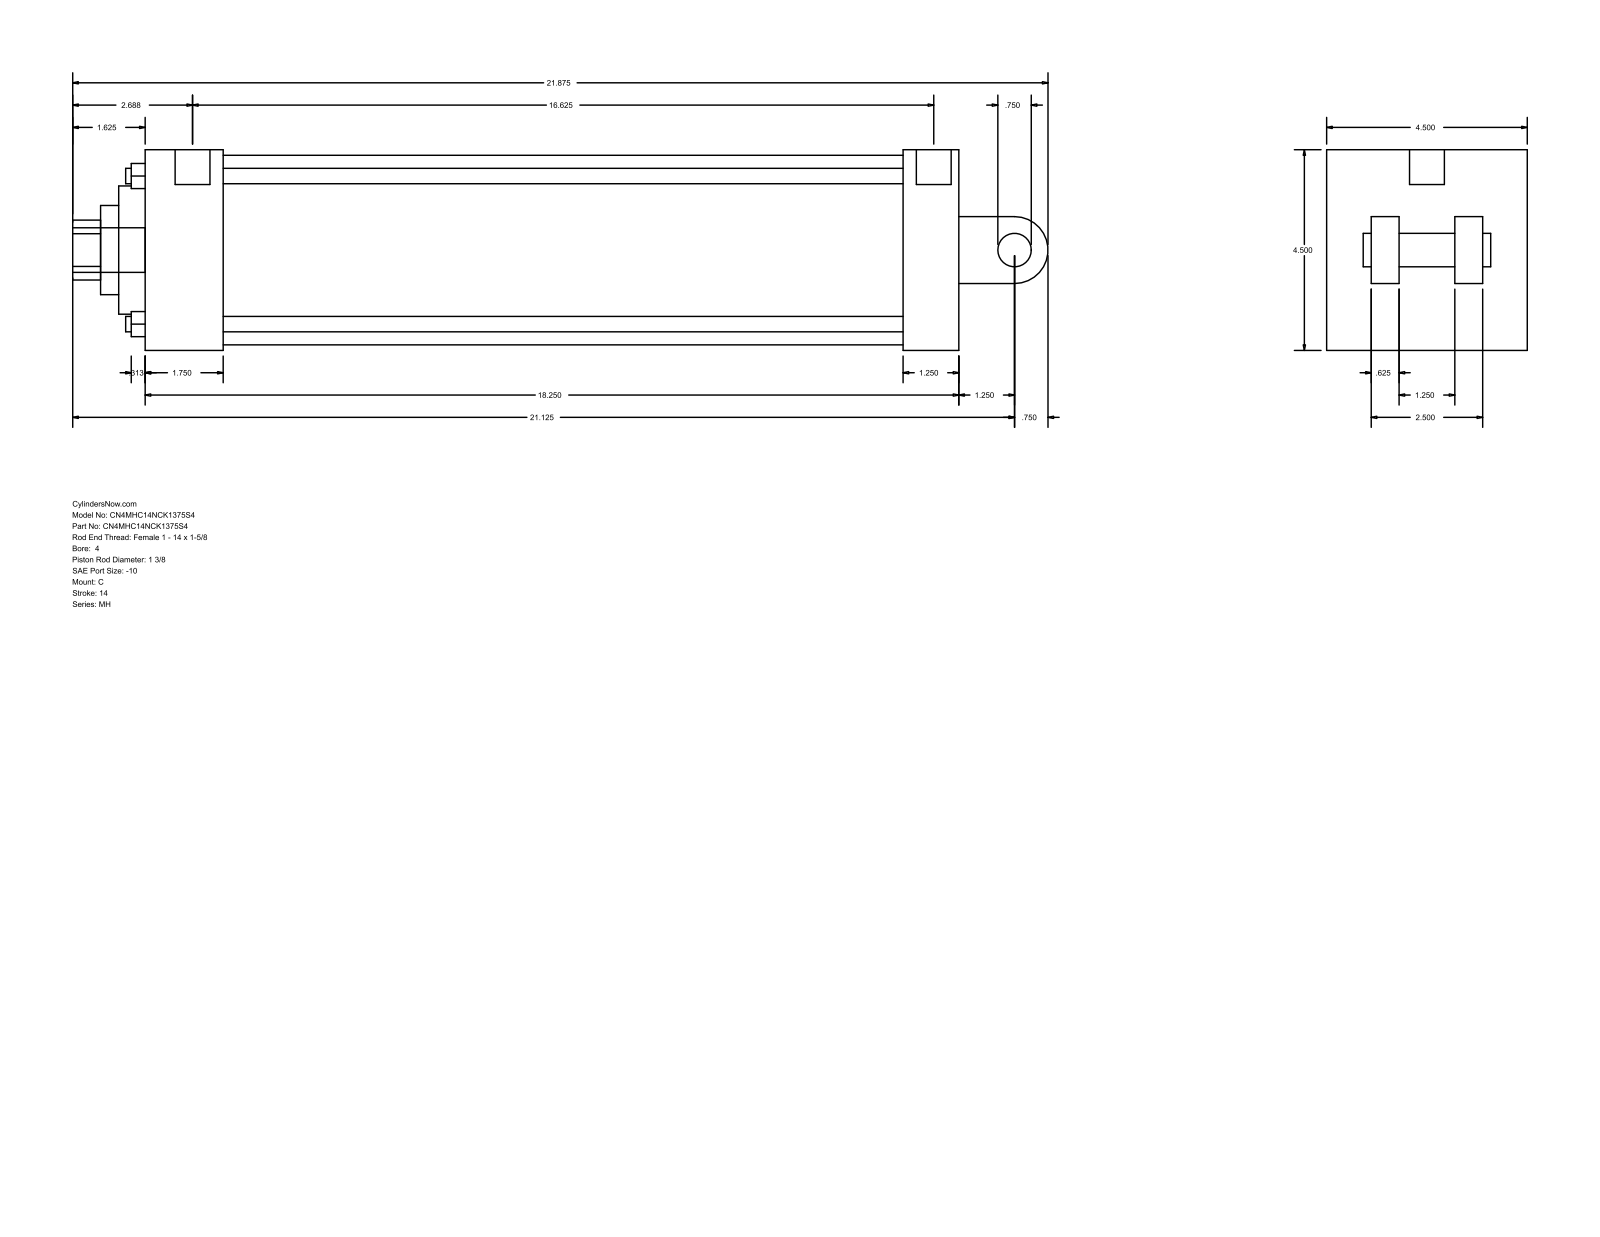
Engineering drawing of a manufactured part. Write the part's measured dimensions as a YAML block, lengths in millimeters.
part_name: "MH_C__0400_1.375"
step_written_by: "GSSL Pune (CONFIG_CONTROL_DESIGN)"
units: millimeters
bodies: {solids: 0, faces: 101, planar: 71, cylindrical: 30, other: 0}
overall_size: [555.62, 114.3, 114.3]
round_holes:
  - {diameter: 8.76, count: 4}
  - {diameter: 8.73, count: 2}
  - {diameter: 19.84, count: 1}
  - {diameter: 34.92, count: 1}
  - {diameter: 50.8, count: 1}
  - {diameter: 73.03, count: 1}
  - {diameter: 107.95, count: 1}
round_bosses_or_shafts:
  - {diameter: 8.73, count: 2}
  - {diameter: 25.4, count: 1}
  - {diameter: 19.84, count: 1}
  - {diameter: 19.05, count: 1}
partial_cylinders:
  - {radius: 17.06, count: 1}
  - {radius: 19.05, count: 1}
face_to_face_distances: [114.3, 463.55, 44.45, 431.8, 387.35, 419.1, 31.75, 73.03, 41.27, 38.1]
hole_center_spacings: [59.62, 84.32, 119.25, 1.58]
